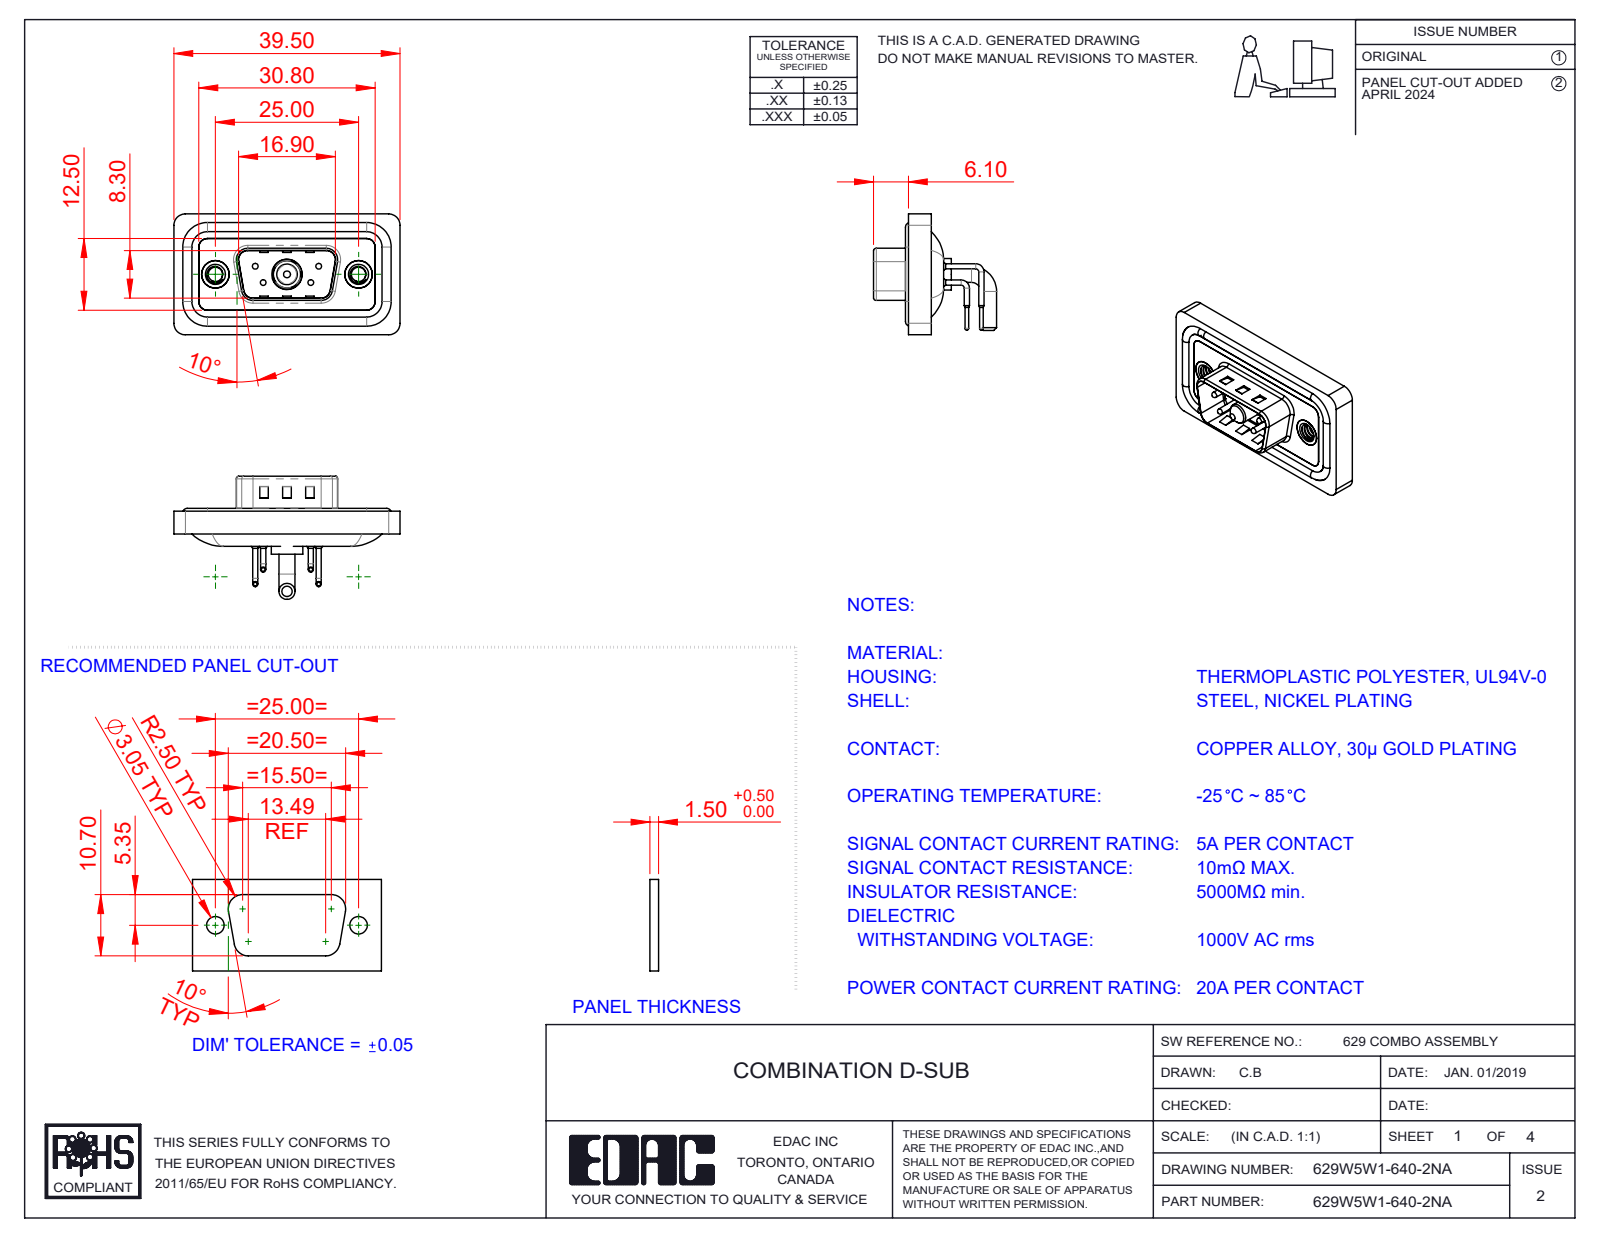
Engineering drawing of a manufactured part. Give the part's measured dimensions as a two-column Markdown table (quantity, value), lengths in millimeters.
| quantity | value |
| --- | --- |
| part name | 629W5W1-640-2NA; 629Combo Contact Row 2; 629Combo Shell Rear_09 Contacts; 629Combo Waterproof Housing_09 Contacts (+5 more) |
| STEP written by | SolidWorks 2023 (CONFIG_CONTROL_DESIGN) |
| units | millimeters |
| bodies | 13 solids, 888 faces (411 planar, 343 cylindrical, 134 other) |
| overall size | 39.5 × 21.5 × 21.1 |
| volume | 4 479 mm³ |
| surface area | 7 167 mm² |
| round holes (diameter × count) | 0.75 × 4, 1.6 × 4, 2 × 4, 2.5 × 2, 4 × 2, 4.8 × 2, 5 × 2, 4.85 × 1, 5.3 × 1 |
| round bosses / shafts (diameter × count) | 0.9 × 8, 1.6 × 4, 1.5 × 4, 1 × 4, 0.65 × 4, 4.9 × 2, 2.8 × 2, 5.5 × 1 |
| partial cylindrical surfaces (radius × count) | 1.5 × 18, 2 × 18, 0.5 × 8, 1.6 × 8, 0.25 × 4, 0.6 × 4, 0.65 × 4, 0.9 × 4 |
| main face-to-face distances | 0.4, 2.9, 1.1, 0.8, 2.1, 2.5, 1.6, 3.1, 4.5, 1.5 |
| hole center spacings | 3.16, 5.72, 7.1, 12.5, 18.1, 4.39, 4.4, 8.31 |
